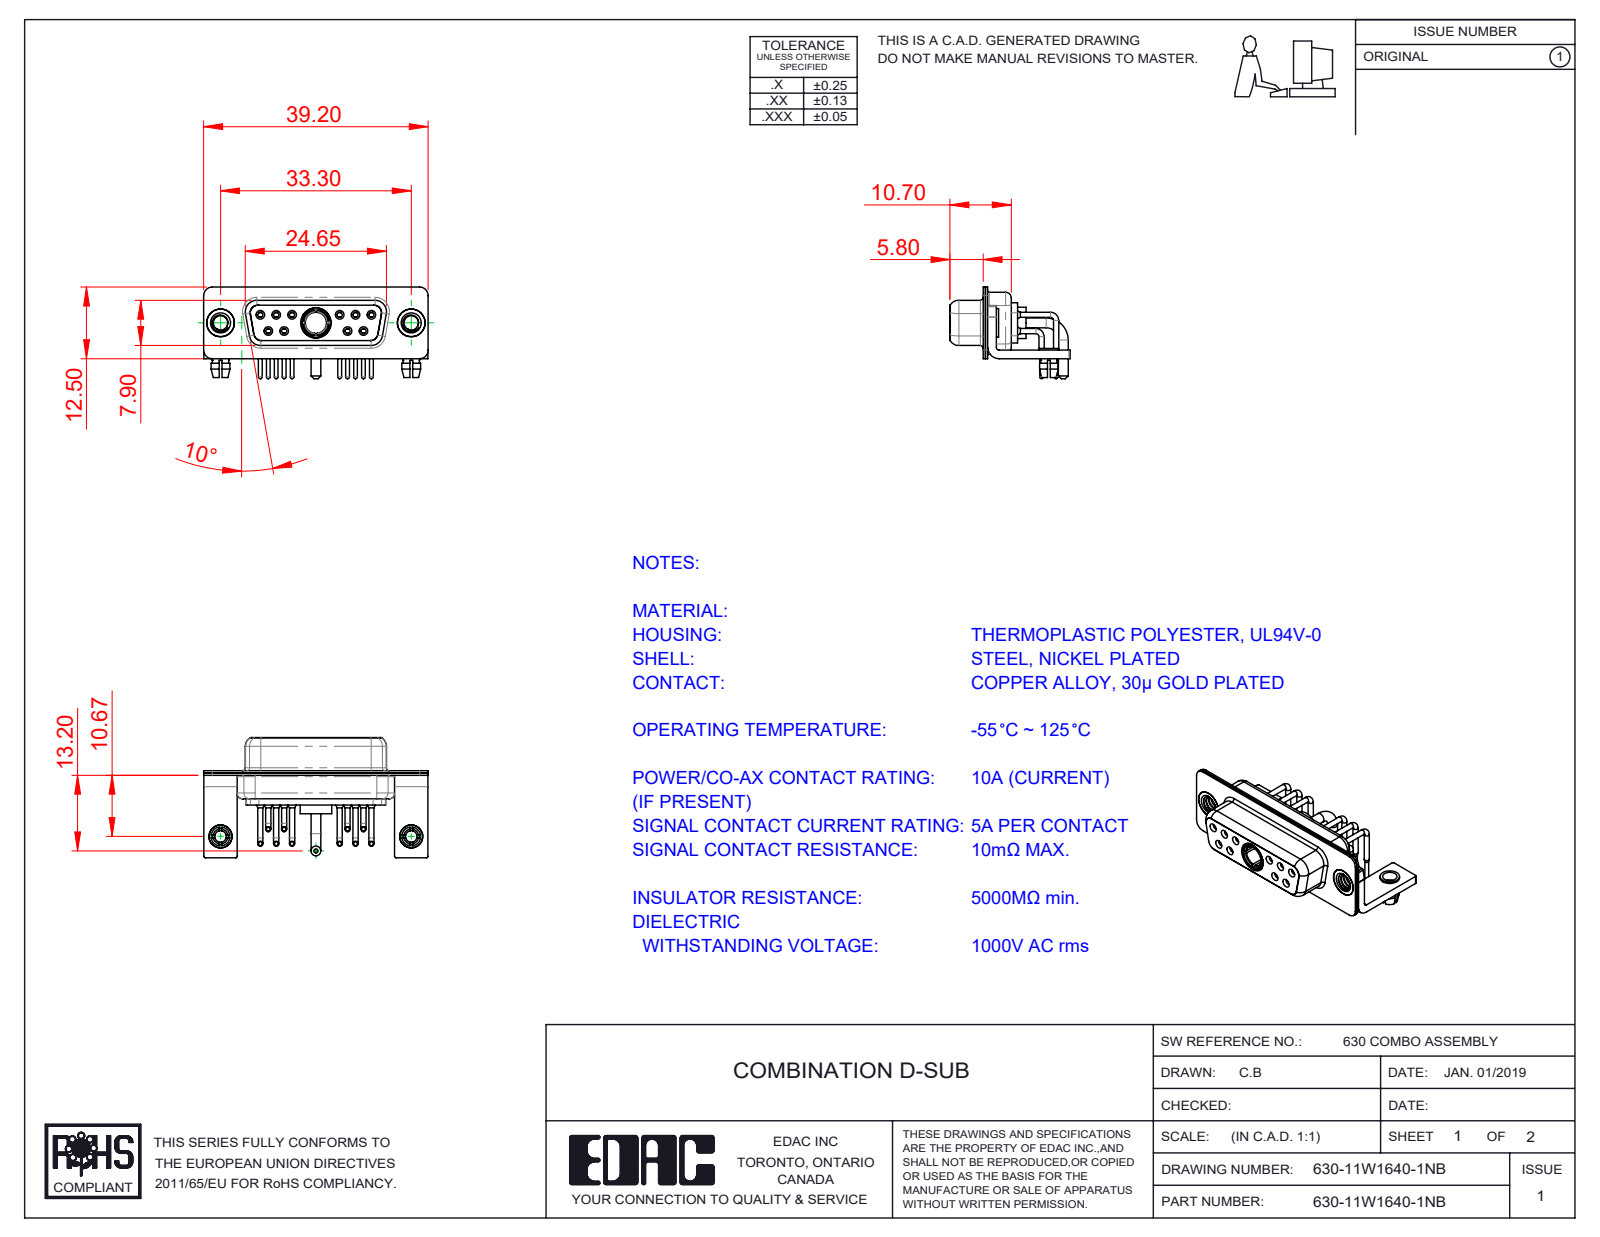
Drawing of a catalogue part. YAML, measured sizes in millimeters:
part_name: "630Combo Stabilizer Bracket; 630Combo Board Lock; 630Combo Shell Rear_15 Contacts; Power Socket_10A RA (+6 more)"
step_written_by: "SolidWorks 2020 (CONFIG_CONTROL_DESIGN)"
units: millimeters
bodies: {solids: 21, faces: 1017, planar: 314, cylindrical: 442, other: 261}
overall_size: [39.2, 21, 16]
volume: 2886
surface_area: 7020
round_holes:
  - {diameter: 2, count: 12}
  - {diameter: 0.9, count: 10}
  - {diameter: 1.1, count: 10}
  - {diameter: 1.5, count: 10}
  - {diameter: 1.7, count: 6}
  - {diameter: 1.6, count: 4}
  - {diameter: 2.5, count: 4}
  - {diameter: 4.85, count: 3}
  - {diameter: 3.2, count: 2}
  - {diameter: 4, count: 2}
  - {diameter: 4.05, count: 2}
  - {diameter: 3.7, count: 1}
round_bosses_or_shafts:
  - {diameter: 0.9, count: 10}
  - {diameter: 0.65, count: 10}
  - {diameter: 1.6, count: 6}
  - {diameter: 5, count: 2}
  - {diameter: 4.95, count: 2}
  - {diameter: 4.8, count: 2}
  - {diameter: 4, count: 2}
  - {diameter: 3.4, count: 2}
partial_cylinders:
  - {radius: 0.25, count: 16}
  - {radius: 1.5, count: 16}
  - {radius: 2, count: 13}
  - {radius: 1.35, count: 12}
  - {radius: 1.6, count: 8}
  - {radius: 0.5, count: 5}
  - {radius: 0.6, count: 4}
  - {radius: 0.65, count: 4}
face_to_face_distances: [0.4, 0.8, 0.45, 1.4, 8.45, 1.5, 1.8, 8.9, 6.2, 2.3]
hole_center_spacings: [3.16, 2.77, 13.85, 11.08, 16.62, 5.03, 5.04, 5.54]
